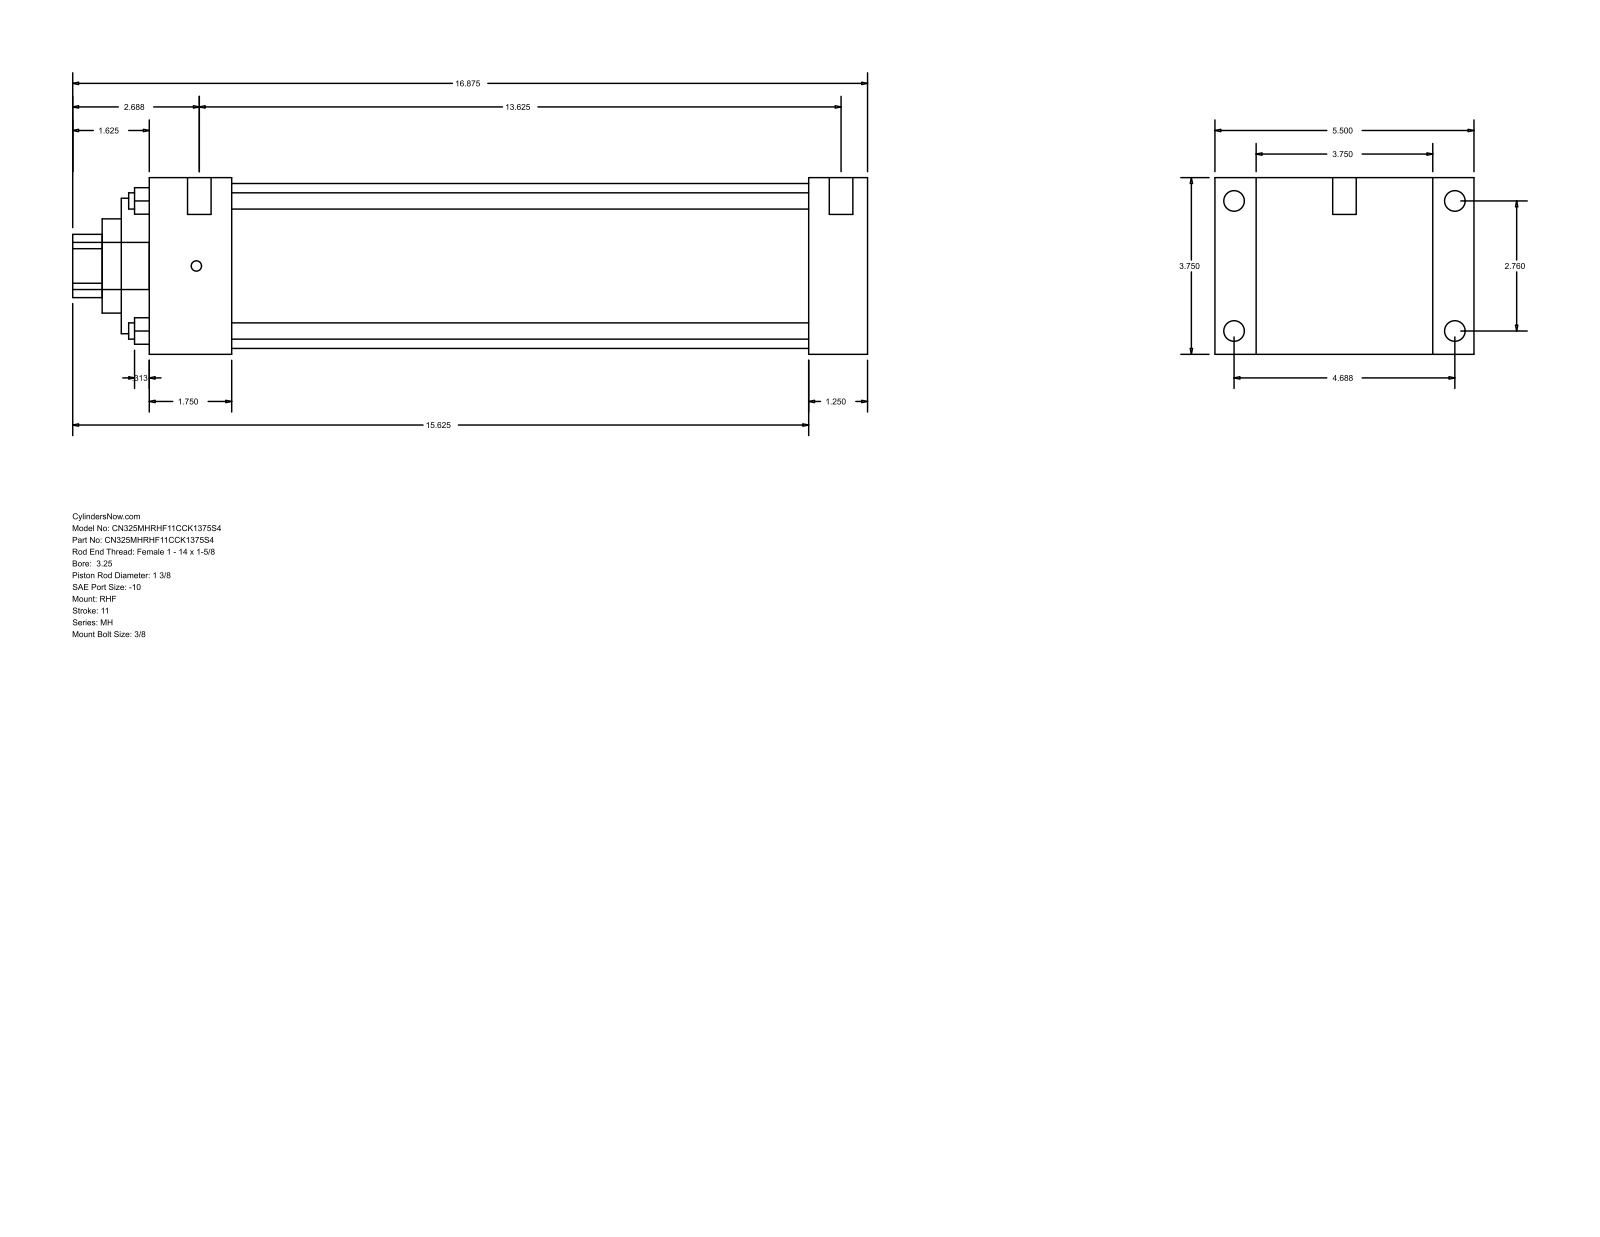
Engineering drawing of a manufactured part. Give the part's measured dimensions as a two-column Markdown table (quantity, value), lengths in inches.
| quantity | value |
| --- | --- |
| part name | MH_RHF__0325_1.375 |
| STEP written by | GSSL Pune (CONFIG_CONTROL_DESIGN) |
| units | inches |
| bodies | 0 solids, 90 faces (61 planar, 29 cylindrical, 0 other) |
| overall size | 16.875 × 5.5 × 3.75 |
| round holes (diameter × count) | 0.345 × 4, 1.375 × 1, 2 × 1, 2.875 × 1, 3.5 × 1 |
| round bosses / shafts (diameter × count) | 0.438 × 4, 0.219 × 4, 0.5 × 2, 1 × 1 |
| partial cylindrical surfaces (radius × count) | 0.672 × 1 |
| main face-to-face distances | 3.75, 1.25, 0.875, 4.625, 14, 15.25, 5.5, 1.75, 12.25, 13.5 |
| hole center spacings | 1.952, 2.76, 3.903 |
